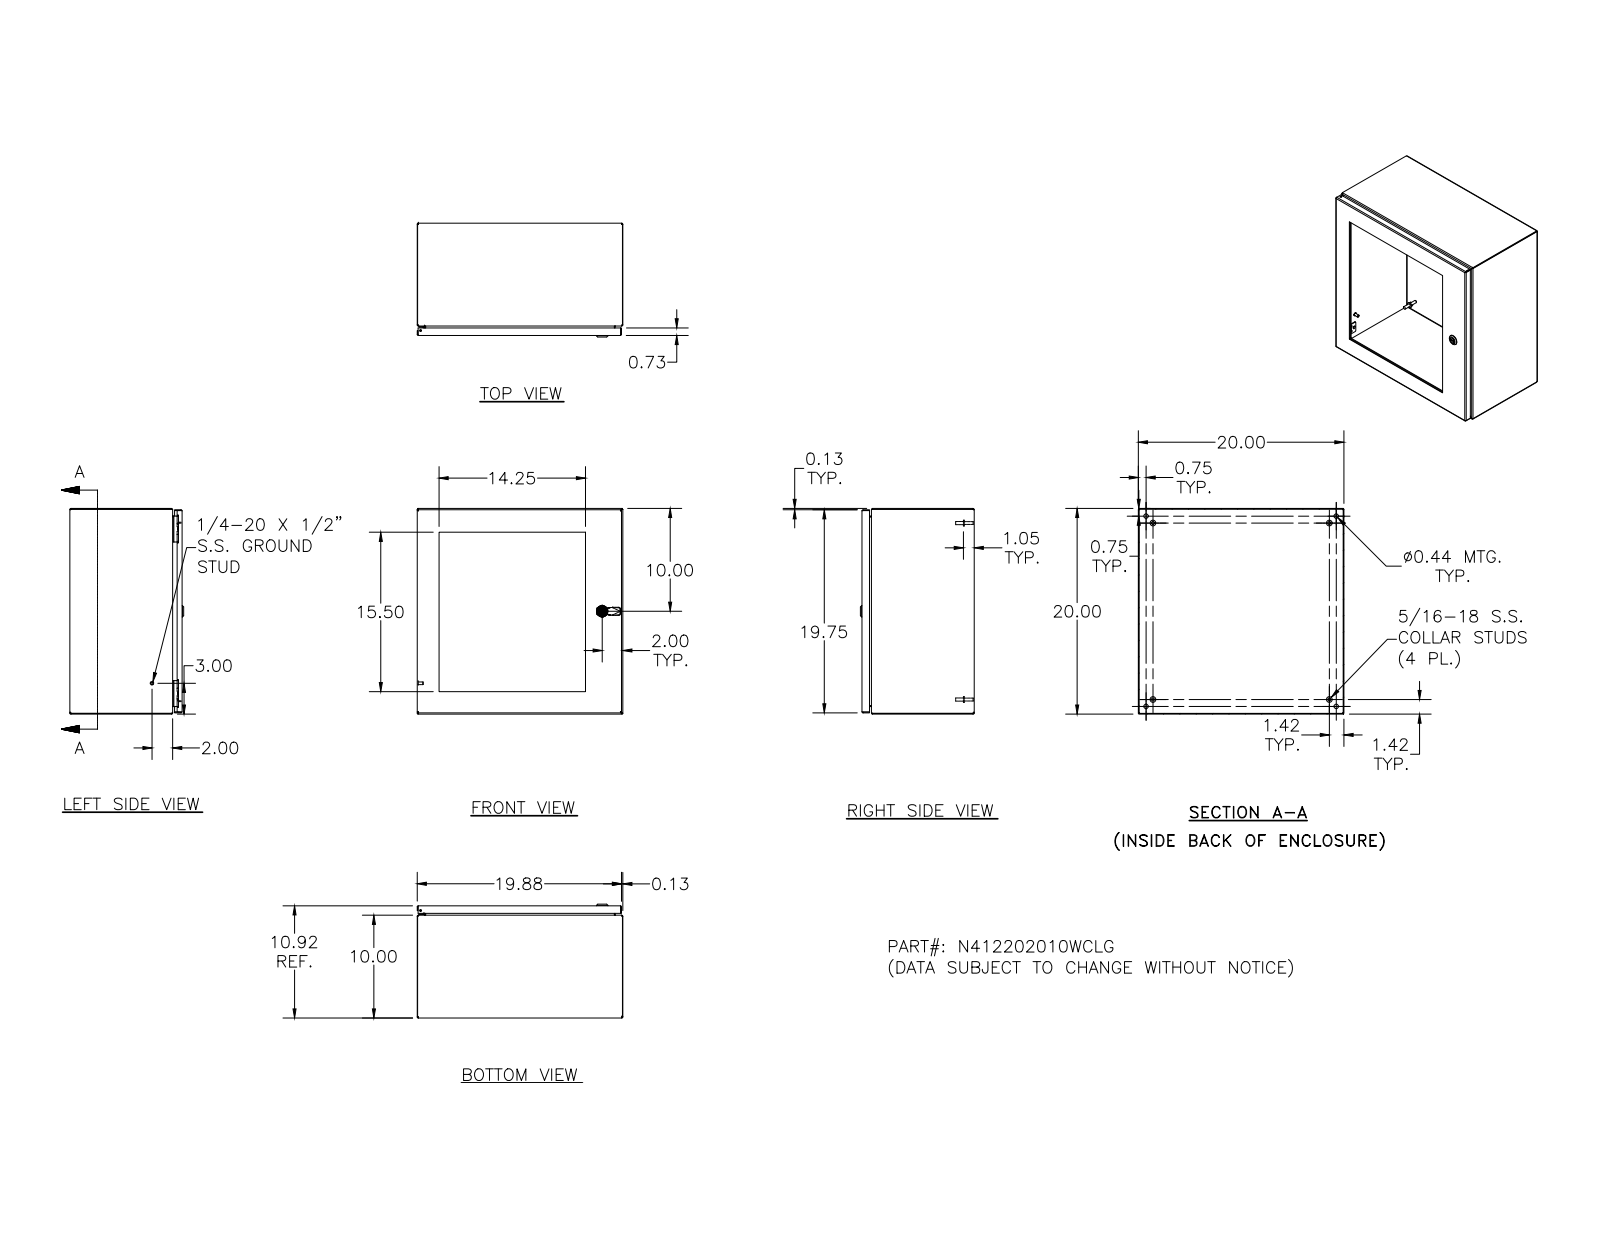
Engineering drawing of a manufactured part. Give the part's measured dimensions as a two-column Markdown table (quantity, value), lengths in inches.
| quantity | value |
| --- | --- |
| part name | N412202010WCLG |
| STEP written by | SolidWorks 2018 (AUTOMOTIVE_DESIGN) |
| units | inches |
| bodies | 69 solids, 2019 faces (753 planar, 617 cylindrical, 649 other) |
| overall size | 20 × 20 × 11.075 |
| volume | 182.3 in³ |
| surface area | 3 784 in² |
| round holes (diameter × count) | 0.156 × 18, 0.281 × 16, 0.188 × 5, 0.093 × 4, 0.152 × 4, 0.167 × 4, 0.172 × 4, 0.437 × 4, 0.187 × 1, 0.197 × 1, 0.315 × 1, 0.394 × 1 |
| round bosses / shafts (diameter × count) | 0.337 × 16, 0.19 × 16, 0.25 × 10, 0.563 × 4, 0.36 × 4, 0.32 × 4, 0.3 × 4, 0.275 × 4 |
| partial cylindrical surfaces (radius × count) | 0.031 × 34, 0.012 × 30, 0.05 × 26, 0.105 × 24, 0.016 × 18, 0.125 × 16, 0.02 × 13, 0.032 × 8 |
| main face-to-face distances | 0.074, 19.926, 10.843, 10.769, 20, 19.852, 0.25, 10.593, 10.519, 10.917 |
| hole center spacings | 4, 8, 16.008, 16, 17.221, 6.221, 8.585, 10.035 |
